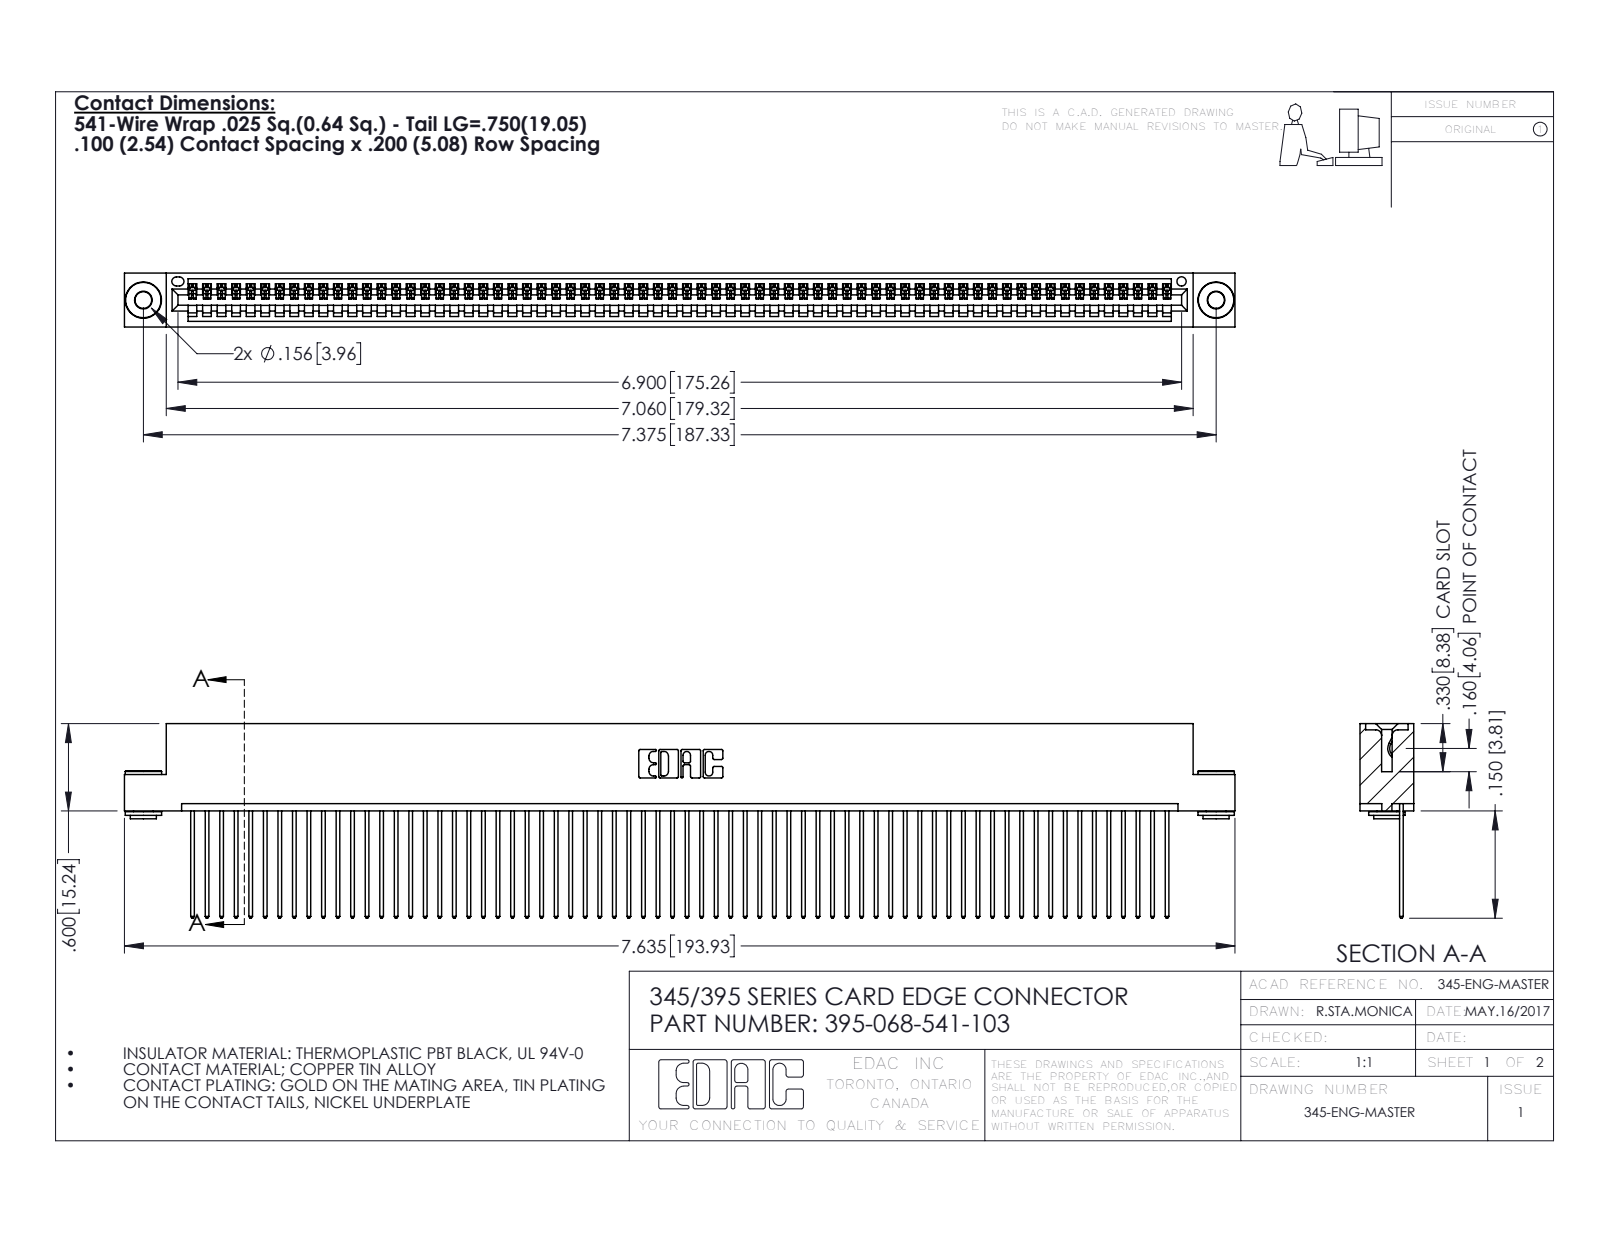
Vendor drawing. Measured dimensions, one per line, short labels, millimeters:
name: 345-250-002_345-250-002-102; 395-068-541-103; 345-292-001_345-293-141; 345 Part_Flush Mounting Lugs - 0.156 Dia-TH
written by: SolidWorks 2016 (CONFIG_CONTROL_DESIGN)
unit: mm
bodies: 71 solids, 4108 faces (2810 planar, 1290 cylindrical, 8 other)
size: 193.9 × 34 × 9.4
volume: 18 880 mm³; area: 26 970 mm²
holes: 2× ⌀2.9, 2× ⌀4, 1× ⌀1.6
bosses: 2× ⌀6.4, 2× ⌀4.6, 2× ⌀3.5
rounds: 136× R0.2, 136× R0.3, 22× R0.3, 6× R0.2, 6× R0.8, 3× R0.7, 2× R0.8, 2× R1
face distances: 1.8, 7.6, 0.6, 2.5, 6.9, 9.4, 5.1, 5.7, 3.8, 1.8
hole spacings: 6.9, 181.3, 187.3
